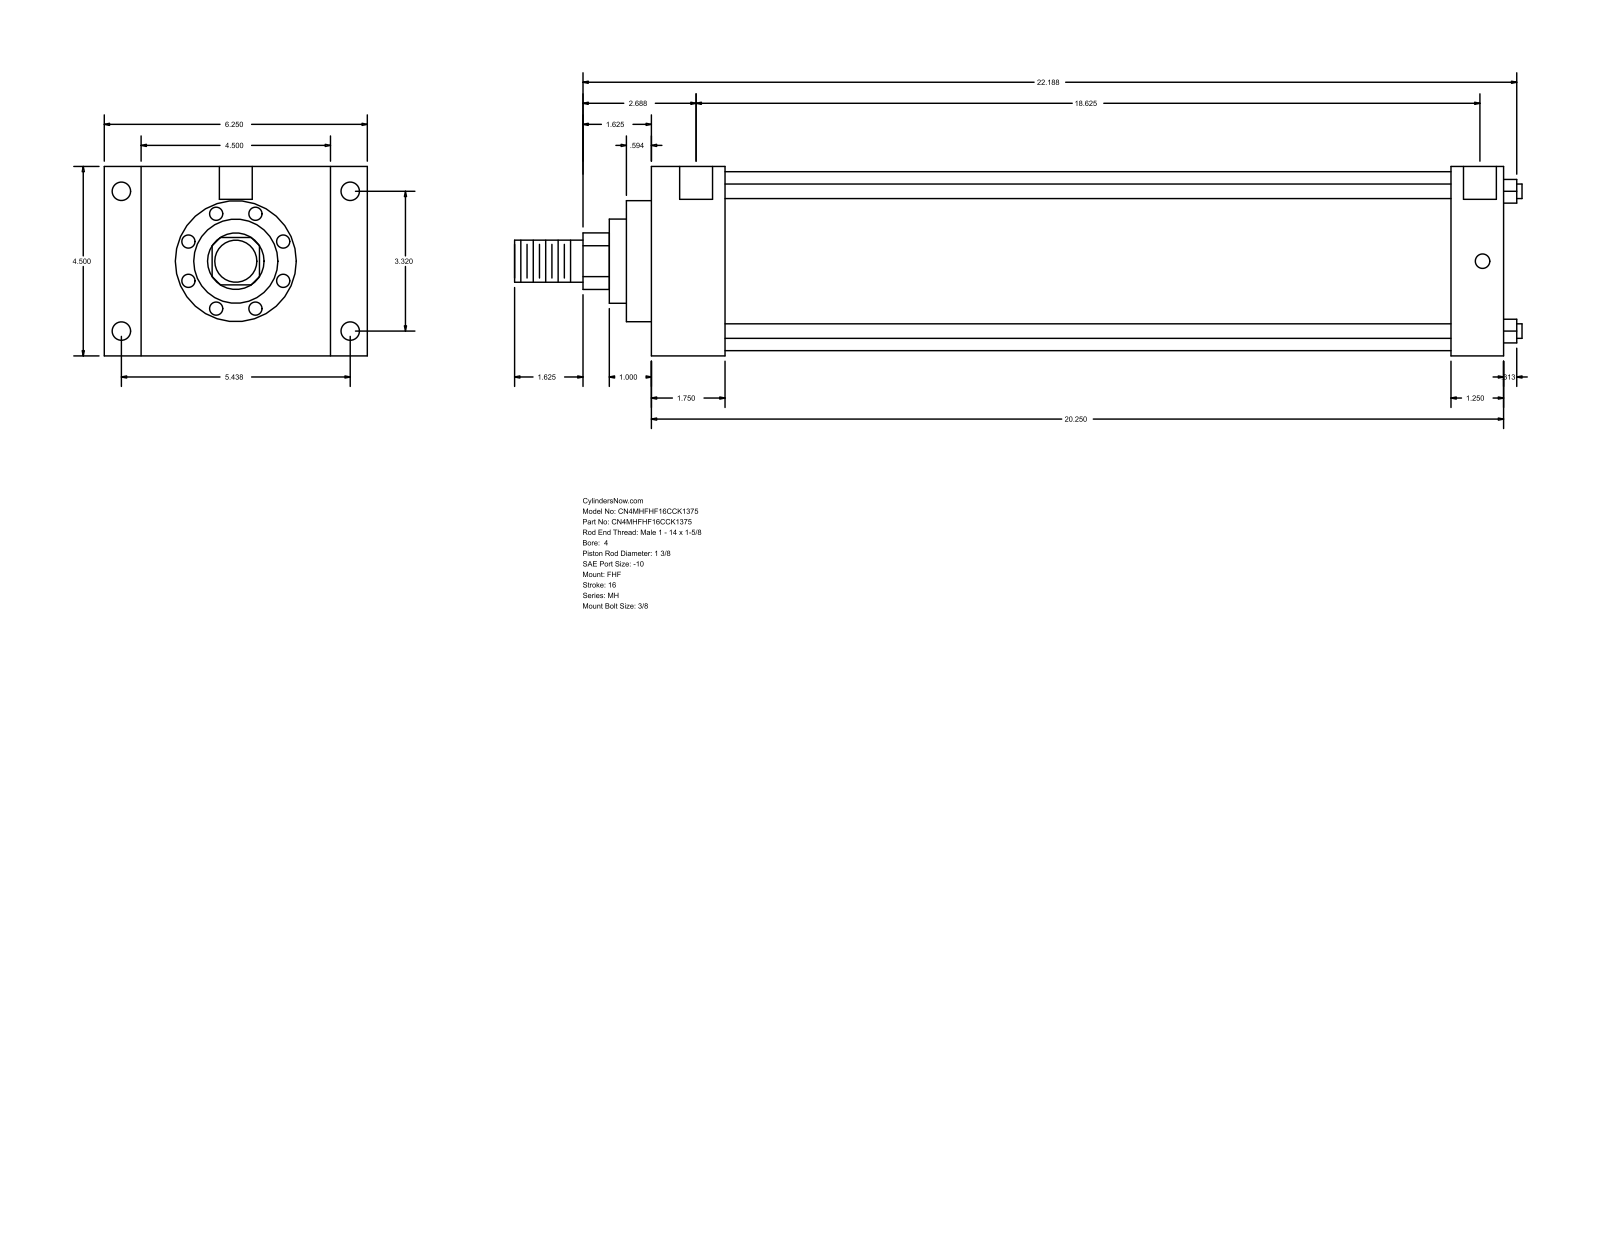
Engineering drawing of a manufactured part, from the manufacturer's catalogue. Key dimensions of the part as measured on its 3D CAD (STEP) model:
Part name (STEP PRODUCT): MH_FHF__0400_1.375
STEP written by: GSSL Pune (CONFIG_CONTROL_DESIGN)
Units: millimetres
Bodies: 0 solids, 90 faces (61 planar, 29 cylindrical, 0 other)
Overall size (bounding box): 608.01 × 158.75 × 114.3
Round holes (diameter × count): ⌀8.73 ×4, ⌀11.13 ×4, ⌀19.84 ×2
Round bosses / shafts (diameter × count): ⌀8.76 ×4, ⌀107.95 ×1, ⌀73.03 ×1, ⌀50.8 ×1, ⌀34.92 ×1, ⌀25.4 ×1
Partial cylindrical surfaces — rounded edges, fillets, slot ends (radius × count): R17.06 ×1
Main face-to-face distances: 114.3, 514.35, 44.45, 469.9, 22.23, 136.53, 158.76, 482.61, 438.16, 31.74
Hole centre spacings: 84.32, 138.12, 161.82, 476.25, 1.58, 1.59, 473.08, 474.66
